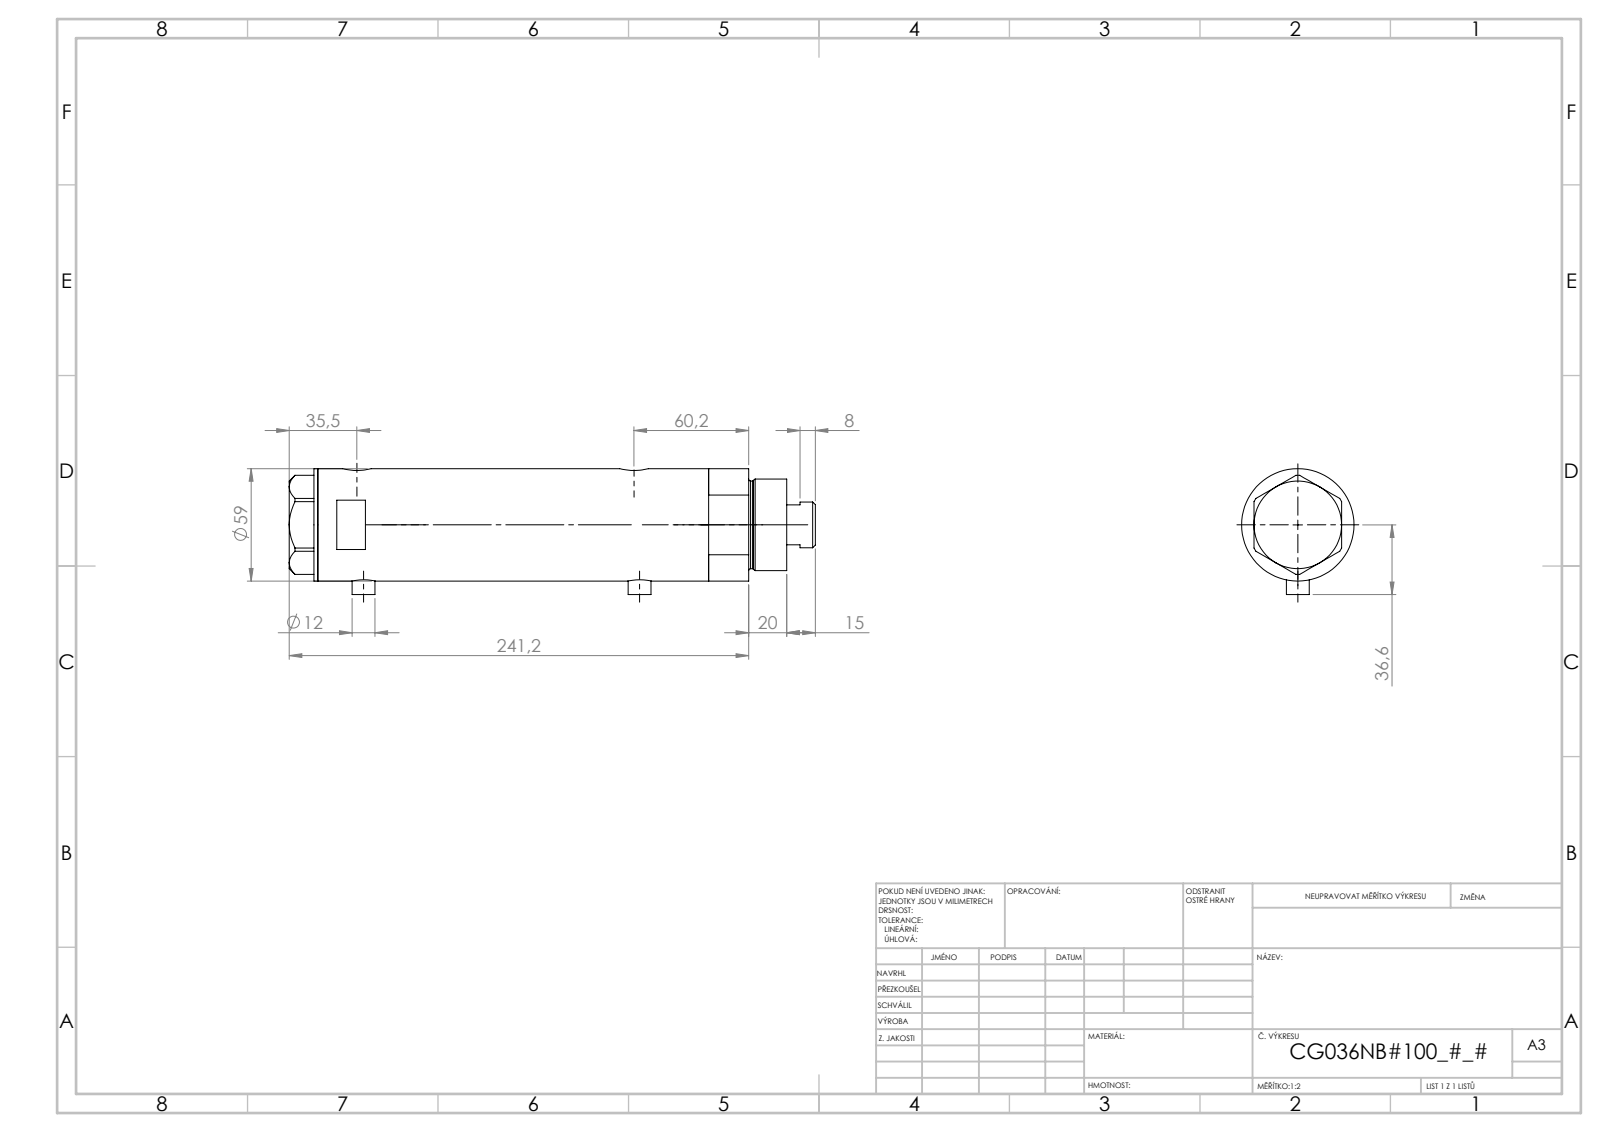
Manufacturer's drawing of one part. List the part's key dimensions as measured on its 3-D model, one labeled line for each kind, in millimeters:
Part name (STEP PRODUCT): V270CG_BACK; V270CG_VC; V270CG_MIDDLE; V270CG_FRONT
STEP written by: SolidWorks 2019 (CONFIG_CONTROL_DESIGN)
Units: millimetres
Bodies: 4 solids, 126 faces (53 planar, 53 cylindrical, 20 other)
Overall size (bounding box): 263.42 × 60.1 × 59
Volume: 591 838 mm³ · Surface area: 119 592 mm²
Round holes (diameter × count): ⌀5 ×2, ⌀9.73 ×2, ⌀12.5 ×2, ⌀15 ×2, ⌀8.5 ×1, ⌀25 ×1, ⌀26.5 ×1, ⌀36 ×1, ⌀40 ×1, ⌀52 ×1
Round bosses / shafts (diameter × count): ⌀12 ×2, ⌀59 ×1, ⌀48 ×1, ⌀46 ×1, ⌀24 ×1
Main face-to-face distances: 157.34, 23.5, 133.84, 15, 38.5, 172.34, 248.42, 233.42, 209.92, 76.08
Hole centre spacings: 2.9, 3.5, 132.15, 135.05, 135.65, 138.55, 2.89, 2.91
